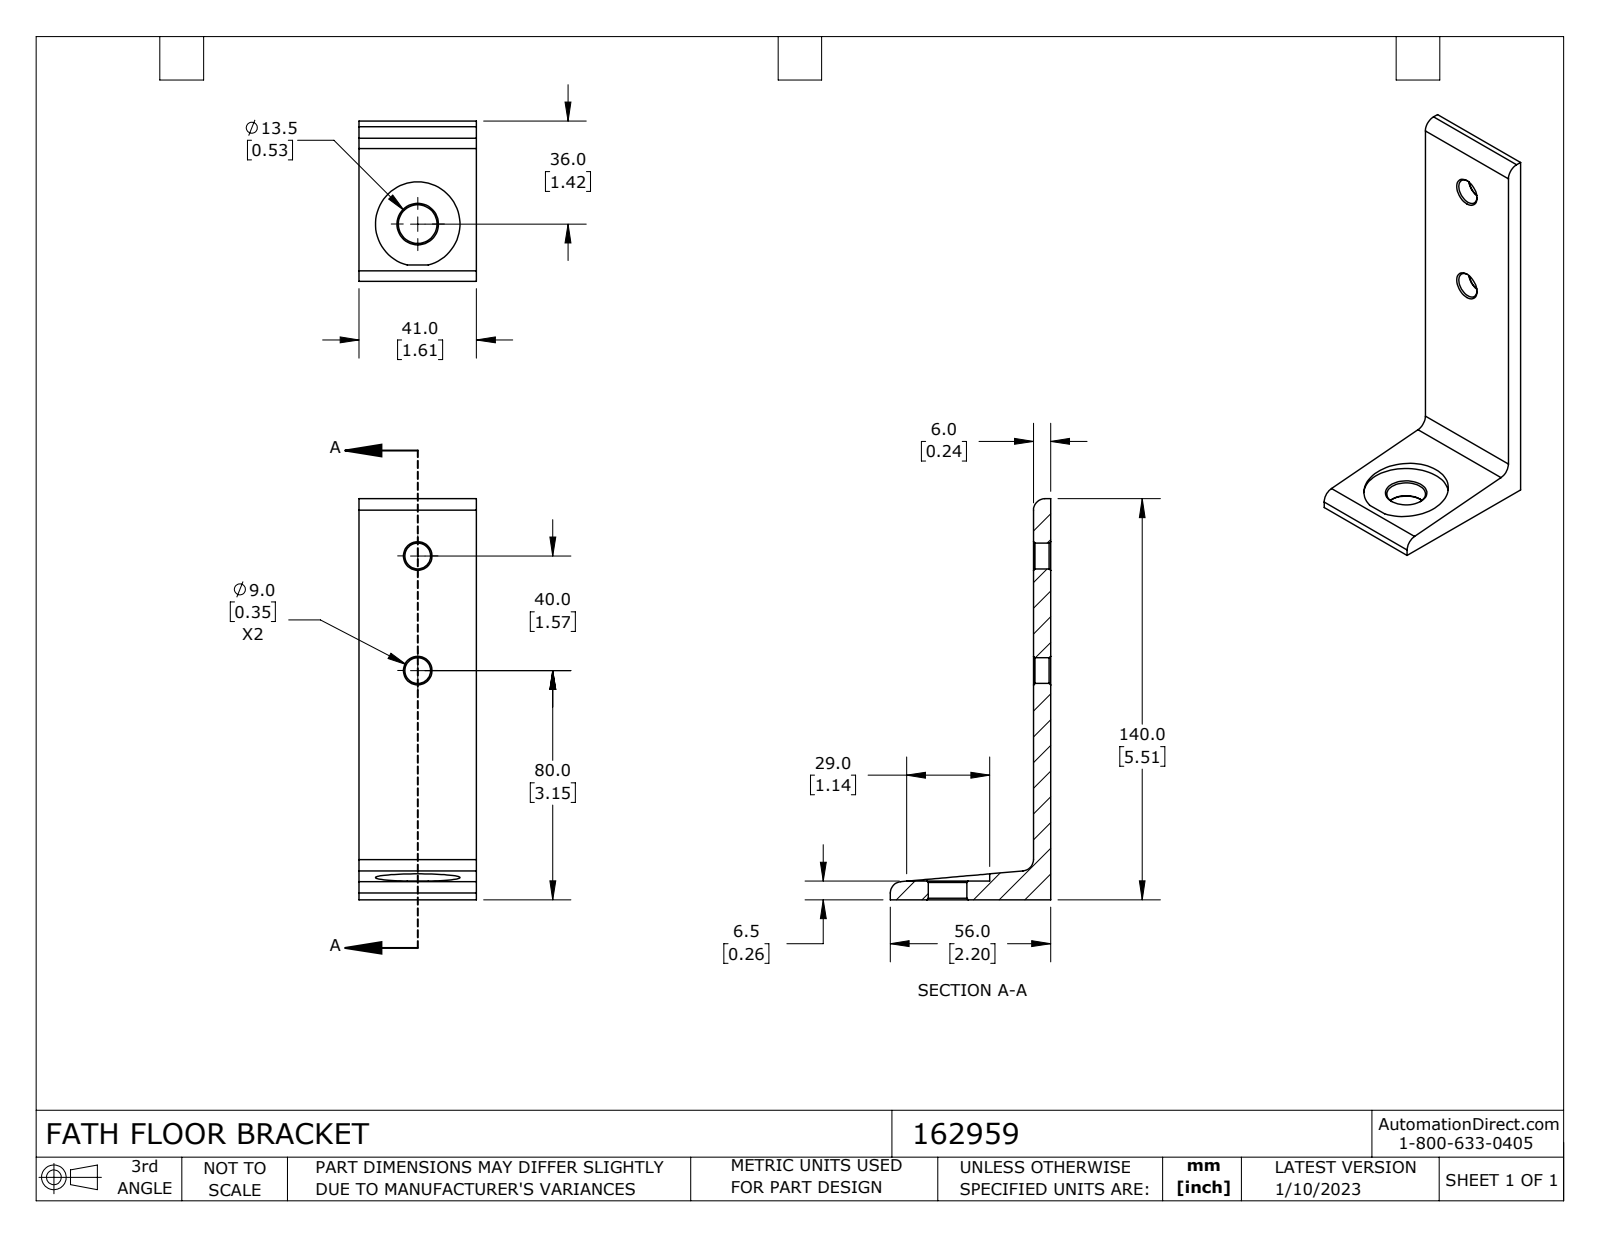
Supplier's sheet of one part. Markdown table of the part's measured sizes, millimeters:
| quantity | value |
| --- | --- |
| part name | 162959 |
| STEP written by | SolidWorks 2021 (CONFIG_CONTROL_DESIGN) |
| units | millimeters |
| bodies | 1 solid, 31 faces (9 planar, 10 cylindrical, 12 other) |
| overall size | 140 × 56 × 41 |
| volume | 48 590 mm³ |
| surface area | 18 340 mm² |
| round holes (diameter × count) | 9 × 2, 13.5 × 1, 29.5 × 1 |
| partial cylindrical surfaces (radius × count) | 4 × 3 |
| main face-to-face distances | 6, 41, 6.5, 56, 50, 140, 133.5 |
| hole center spacings | 40 |
